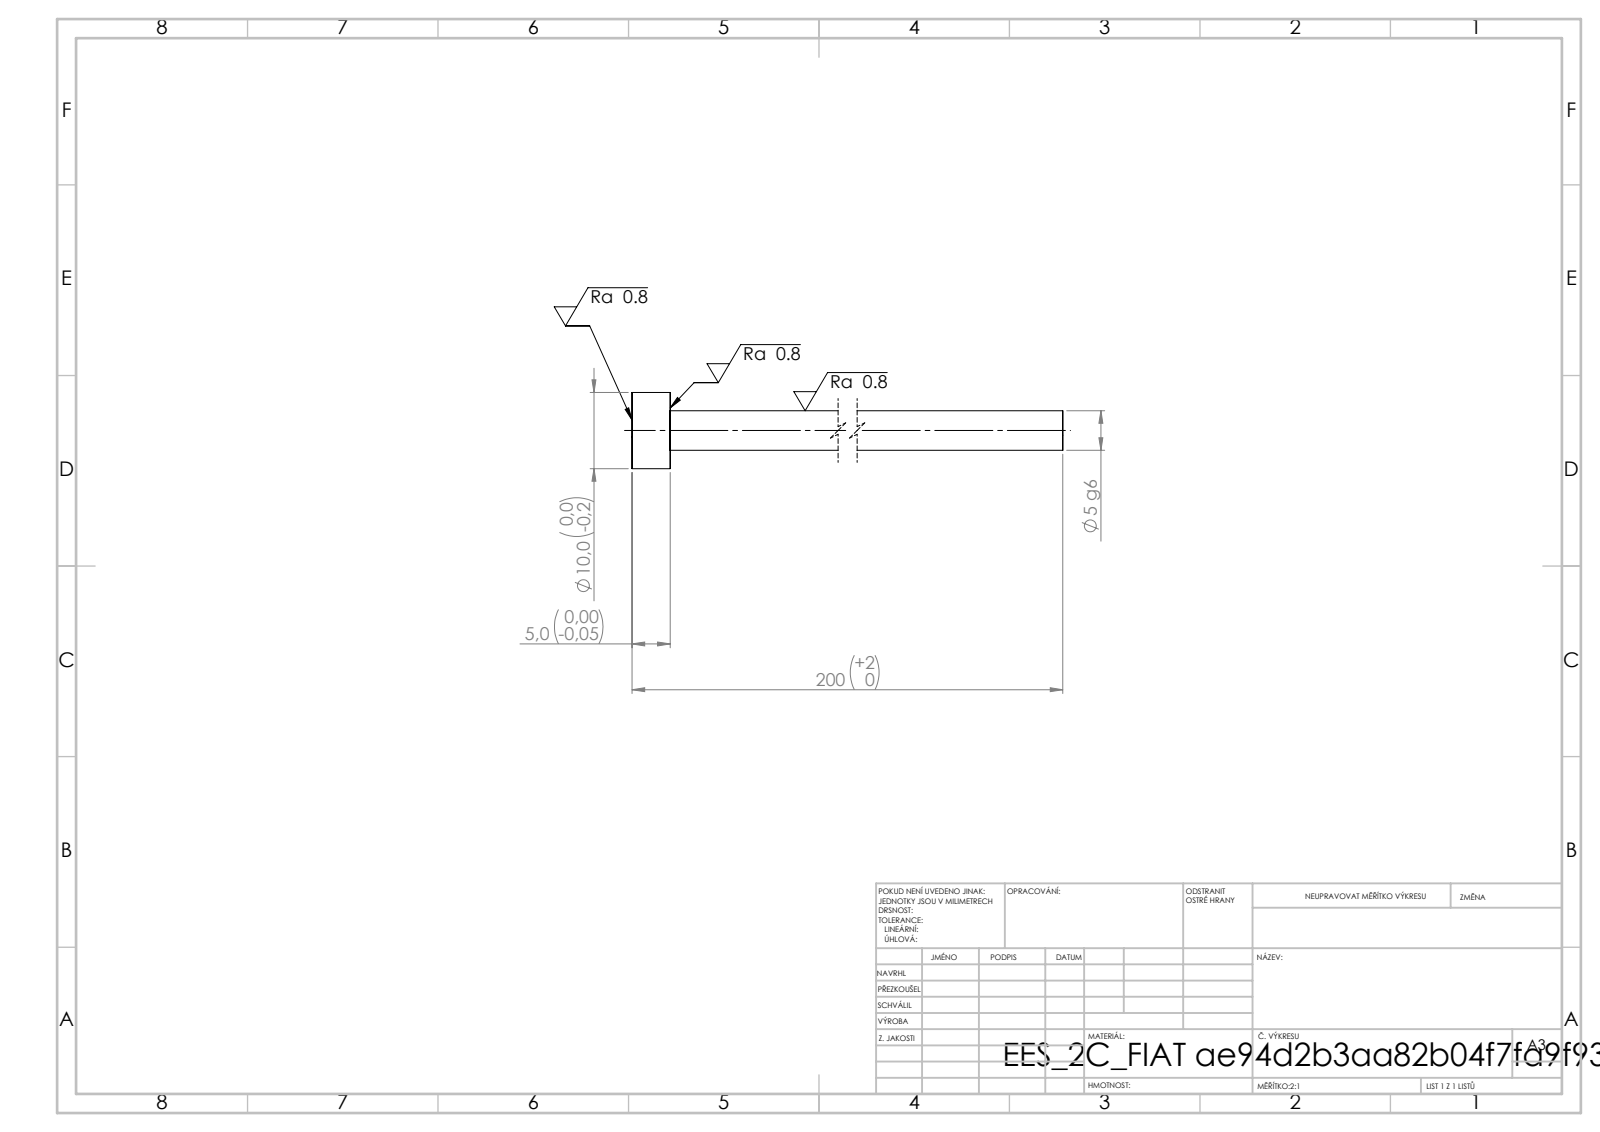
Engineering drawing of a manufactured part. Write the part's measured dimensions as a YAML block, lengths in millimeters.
step_written_by: "SolidWorks 2019 (CONFIG_CONTROL_DESIGN)"
units: millimeters
bodies: {solids: 1, faces: 7, planar: 3, cylindrical: 4, other: 0}
overall_size: [200, 10, 10]
volume: 4534
surface_area: 3500
round_bosses_or_shafts:
  - {diameter: 10, count: 1}
  - {diameter: 5.2, count: 1}
face_to_face_distances: [5, 200, 195]
